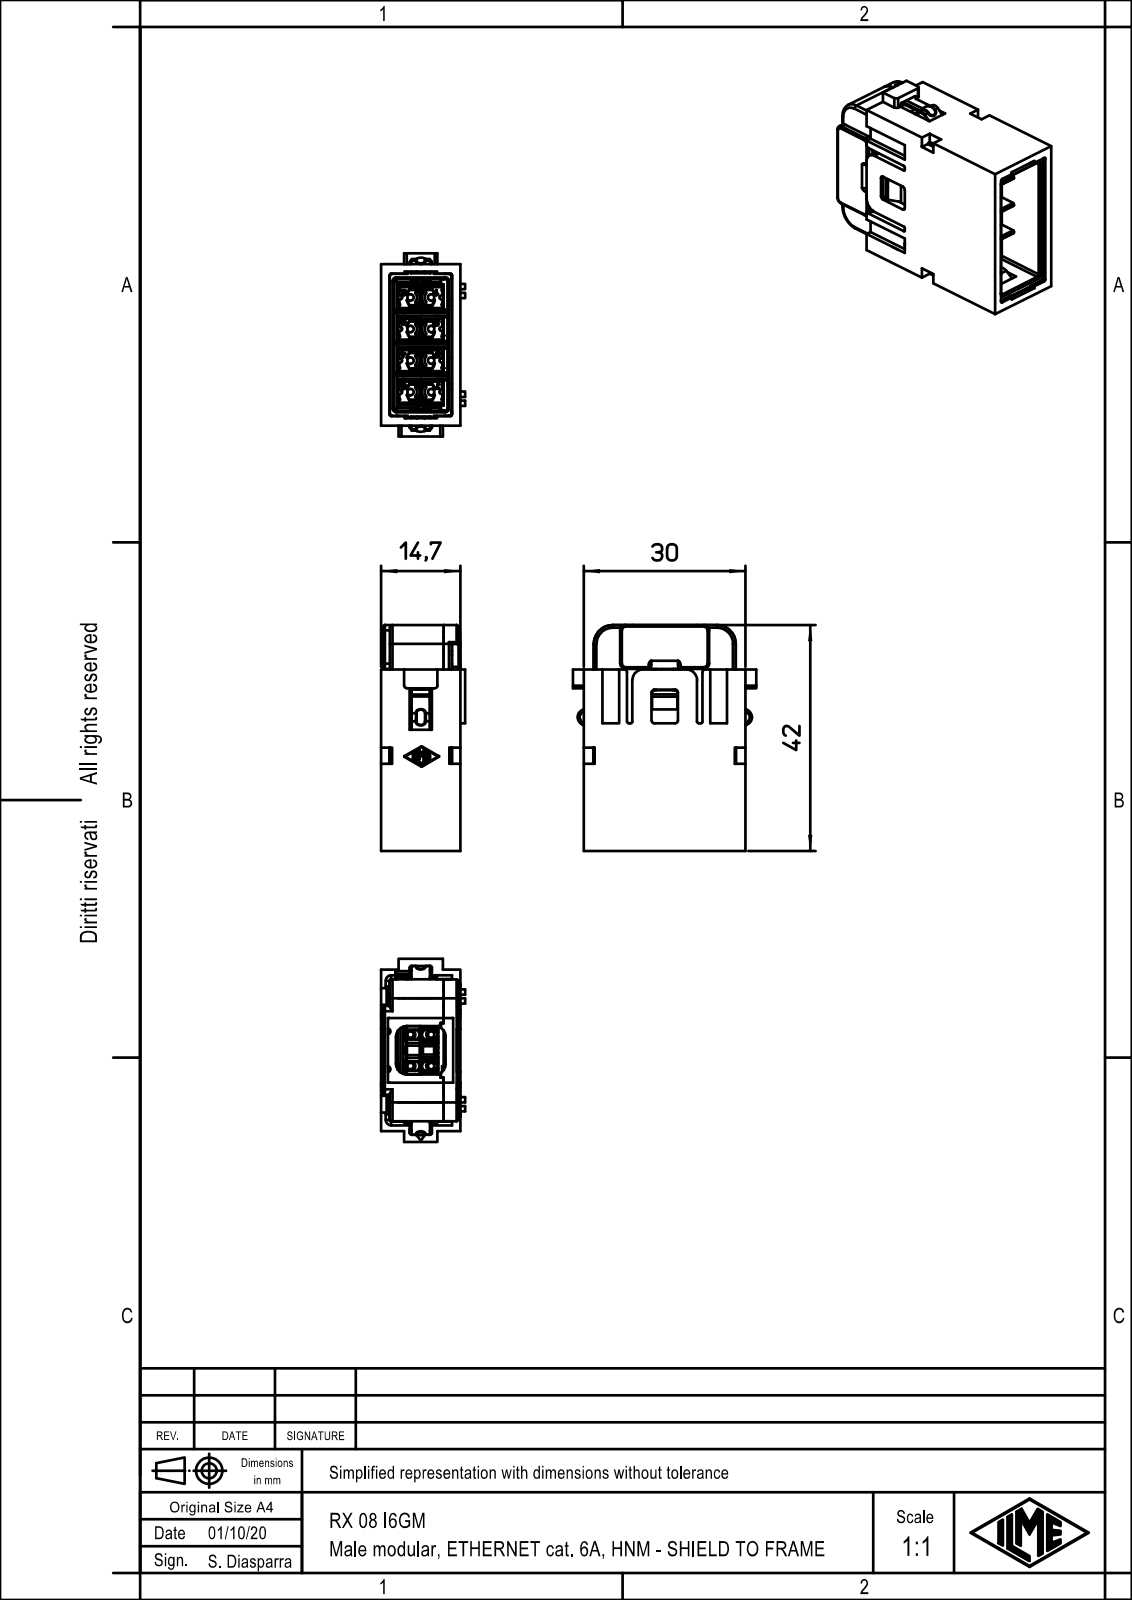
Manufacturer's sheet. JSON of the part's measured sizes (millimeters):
{"part_name": "CX_08_I6GM", "step_written_by": "Creo Elements/Direct Modeling 20.1B 02-Apr-2019 (C) Parametric Technology GmbH (AUTOMOTIVE_DESIGN)", "units": "millimeters", "bodies": {"solids": 1, "faces": 648, "planar": 546, "cylindrical": 65, "other": 37}, "overall_size": [41.95, 34, 15.6], "volume_mm3": 14029, "surface_area_mm2": 6988, "round_holes": [[1, 8], [5, 2]], "round_bosses_or_shafts": [[4.7, 2]], "partial_cylinders_radius": [[0.5, 10], [1, 10], [0.3, 8], [0.1, 5], [1.15, 2], [3.5, 2]], "face_to_face_distances": [14.7, 2.4, 12.3, 30, 1, 2, 14.3, 13.1, 0.4, 9], "hole_center_spacings": [5.85, 6.98, 3.8, 11.7, 12.3, 17.55, 17.96, 19.6]}
